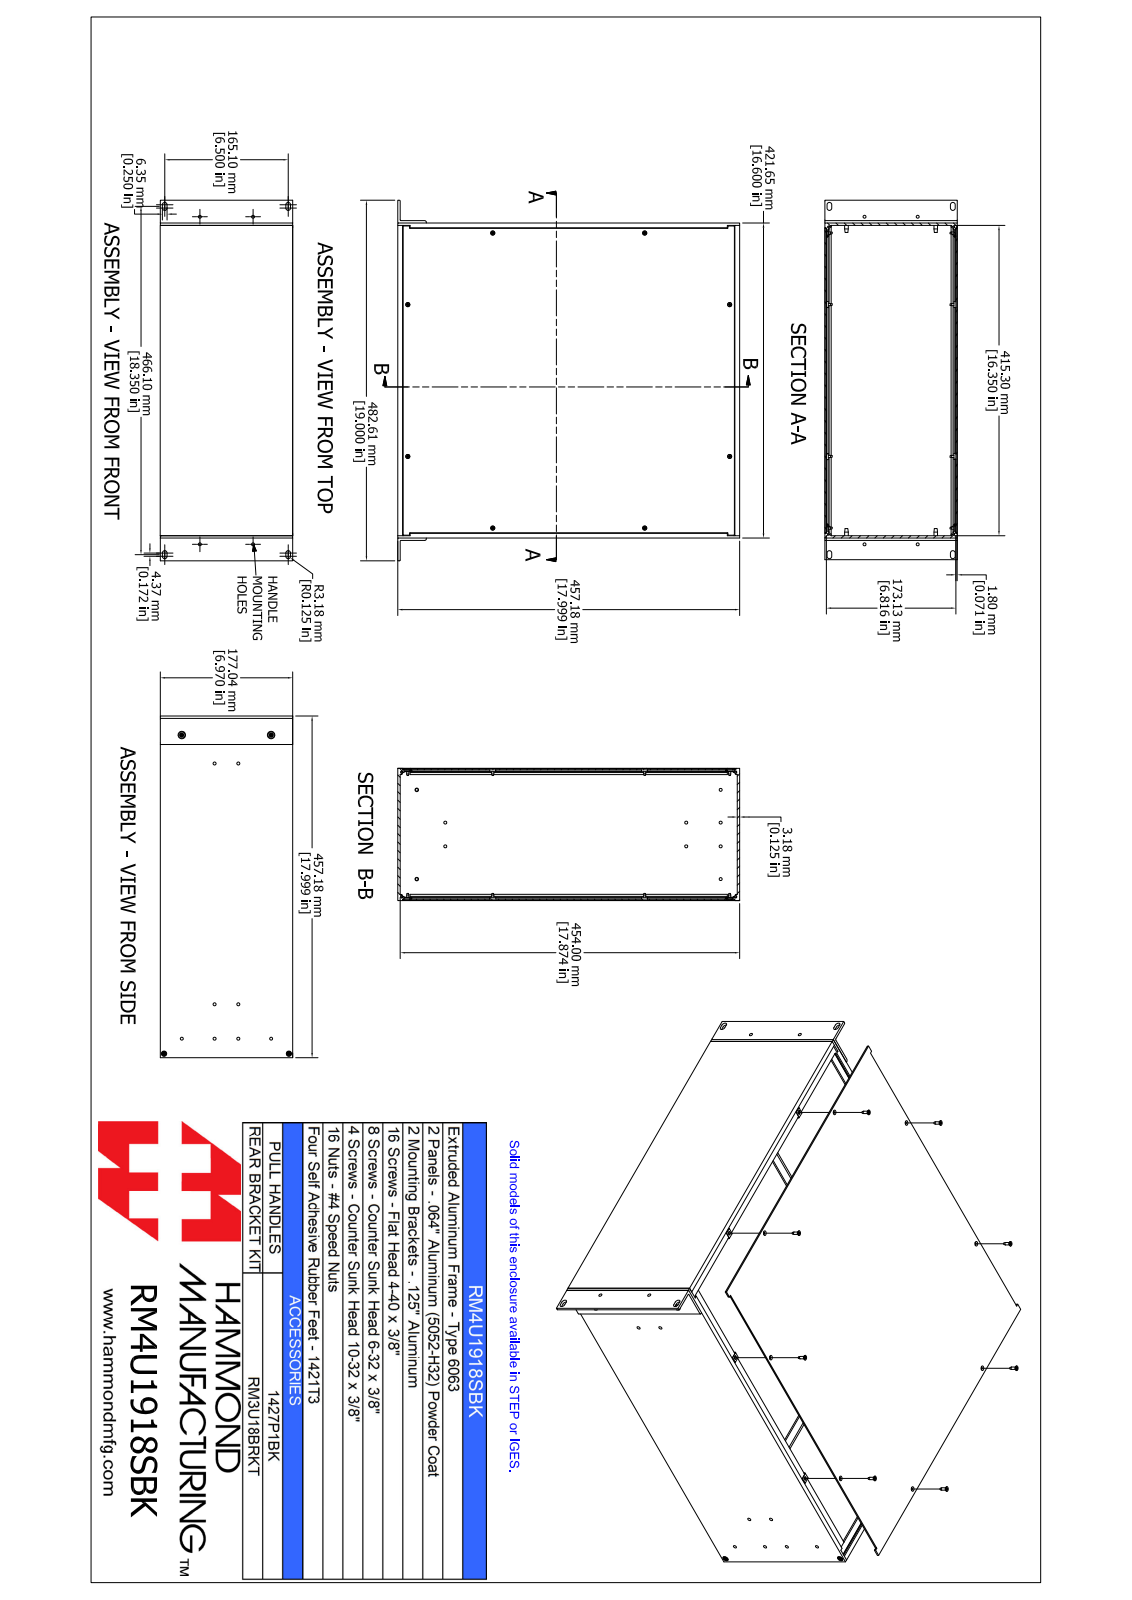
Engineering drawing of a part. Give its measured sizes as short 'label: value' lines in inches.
name: RM4U1918SBK
written by: SolidWorks 2021 (AUTOMOTIVE_DESIGN)
unit: in
bodies: 52 solids, 1384 faces (636 planar, 252 cylindrical, 496 other)
size: 19 × 17.999 × 6.971
volume: 112.8 in³; area: 2 367 in²
holes: 9× ⌀0.118, 8× ⌀0.098, 8× ⌀0.157, 6× ⌀0.159, 4× ⌀0.138, 4× ⌀0.156, 4× ⌀0.157, 4× ⌀0.165, 4× ⌀0.169, 2× ⌀0.197
bosses: 10× ⌀0.214, 10× ⌀0.112, 4× ⌀0.238, 4× ⌀0.138, 2× ⌀0.333, 2× ⌀0.19
rounds: 22× R0.039, 16× R0.015, 16× R0.038, 16× R0.049, 8× R0.055, 8× R0.125, 8× R0.131, 2× R0.079
face distances: 0.071, 6.887, 0.125, 6.816, 6.958, 16.475, 16.6, 0.125, 16.35, 17.874
hole spacings: 8, 12.593, 5.851, 5.851, 13.03, 16.815, 17.151, 1.224
